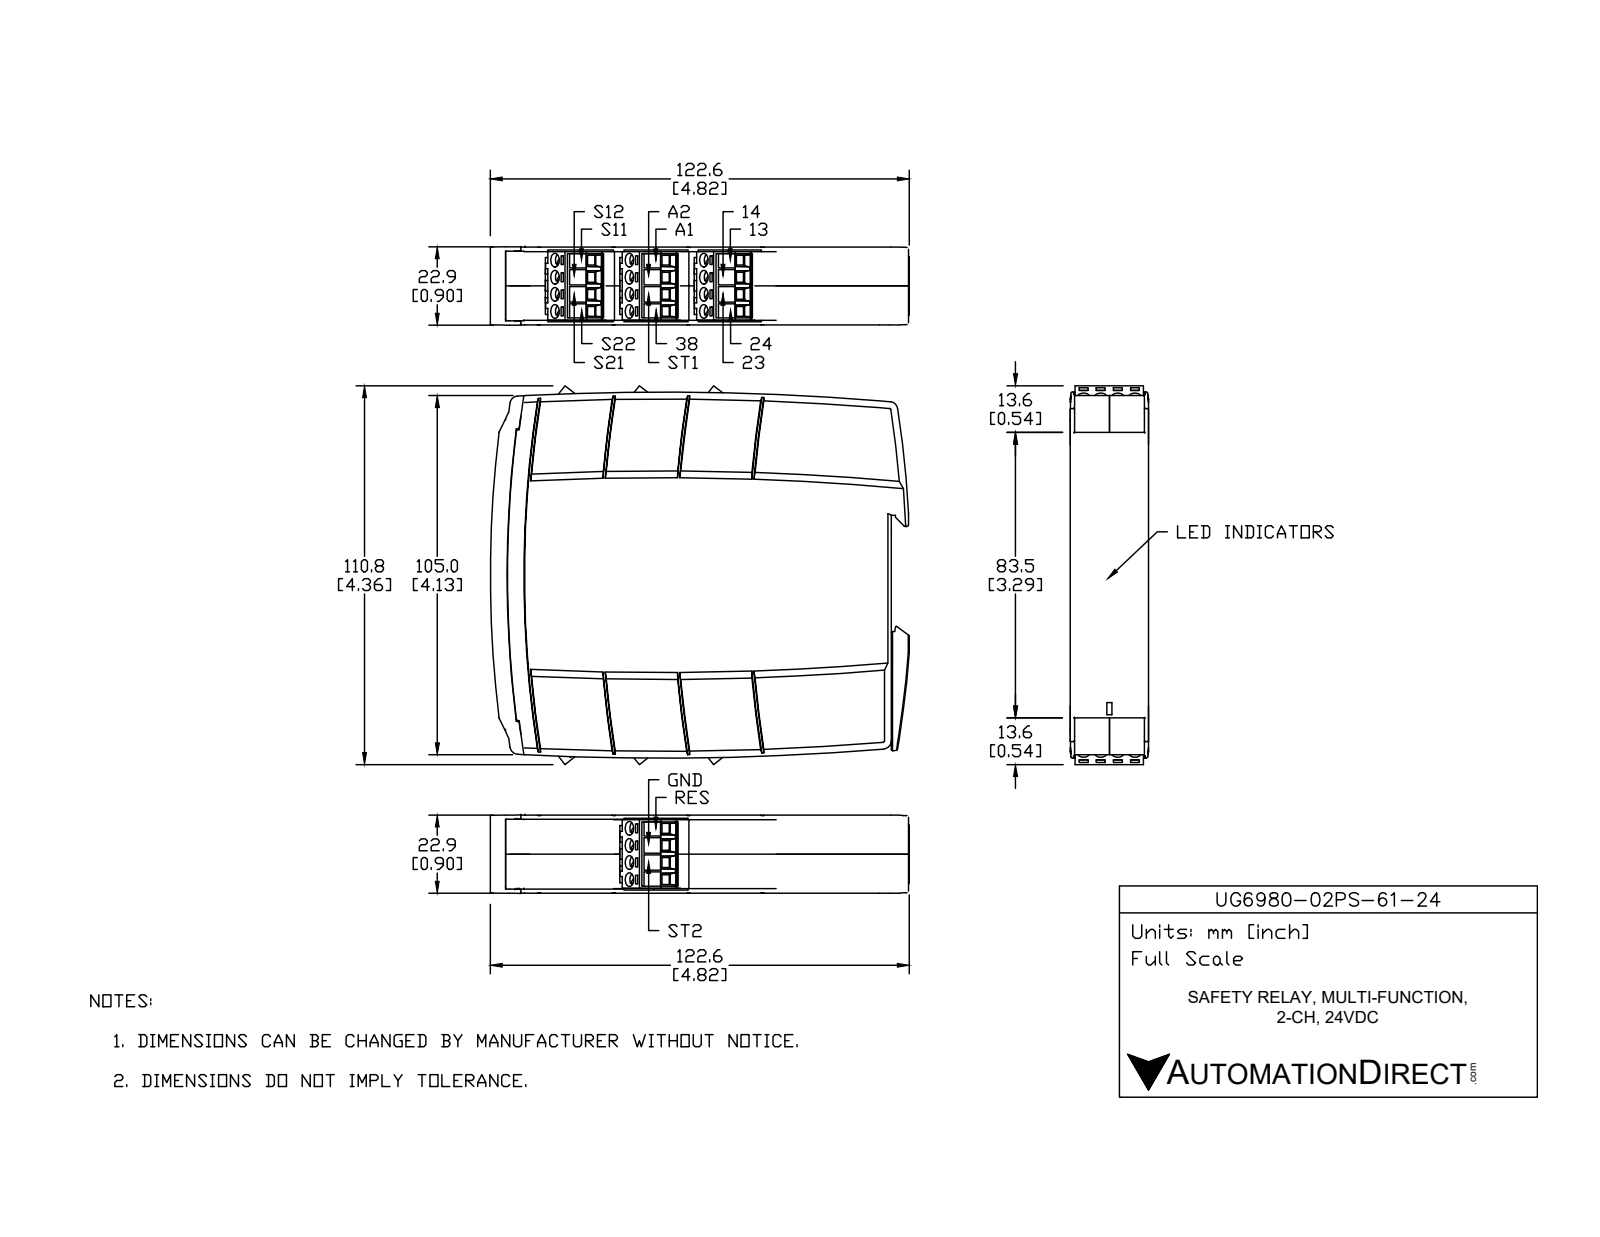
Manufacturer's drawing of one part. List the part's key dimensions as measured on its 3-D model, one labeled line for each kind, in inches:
Part name (STEP PRODUCT): UG6980-02PS-61-24
STEP written by: SolidWorks 2021 (AUTOMOTIVE_DESIGN)
Units: inches
Bodies: 1 solid, 403 faces (356 planar, 38 cylindrical, 9 other)
Overall size (bounding box): 4.813 × 4.355 × 0.886
Volume: 16.69 in³ · Surface area: 58.39 in²
Round holes (diameter × count): ⌀0.157 ×16
Partial cylindrical surfaces — rounded edges, fillets, slot ends (radius × count): R0.012 ×9, R0.094 ×7, R0.02 ×2, R31.496 ×2
Main face-to-face distances: 0.886, 0.049, 0.837, 0.675, 0.528, 0.787, 0.567, 1.35, 1.056, 1.242
Hole centre spacings: 0.197, 0.394, 0.563, 0.563, 1.074, 0.528, 0.528, 0.591
